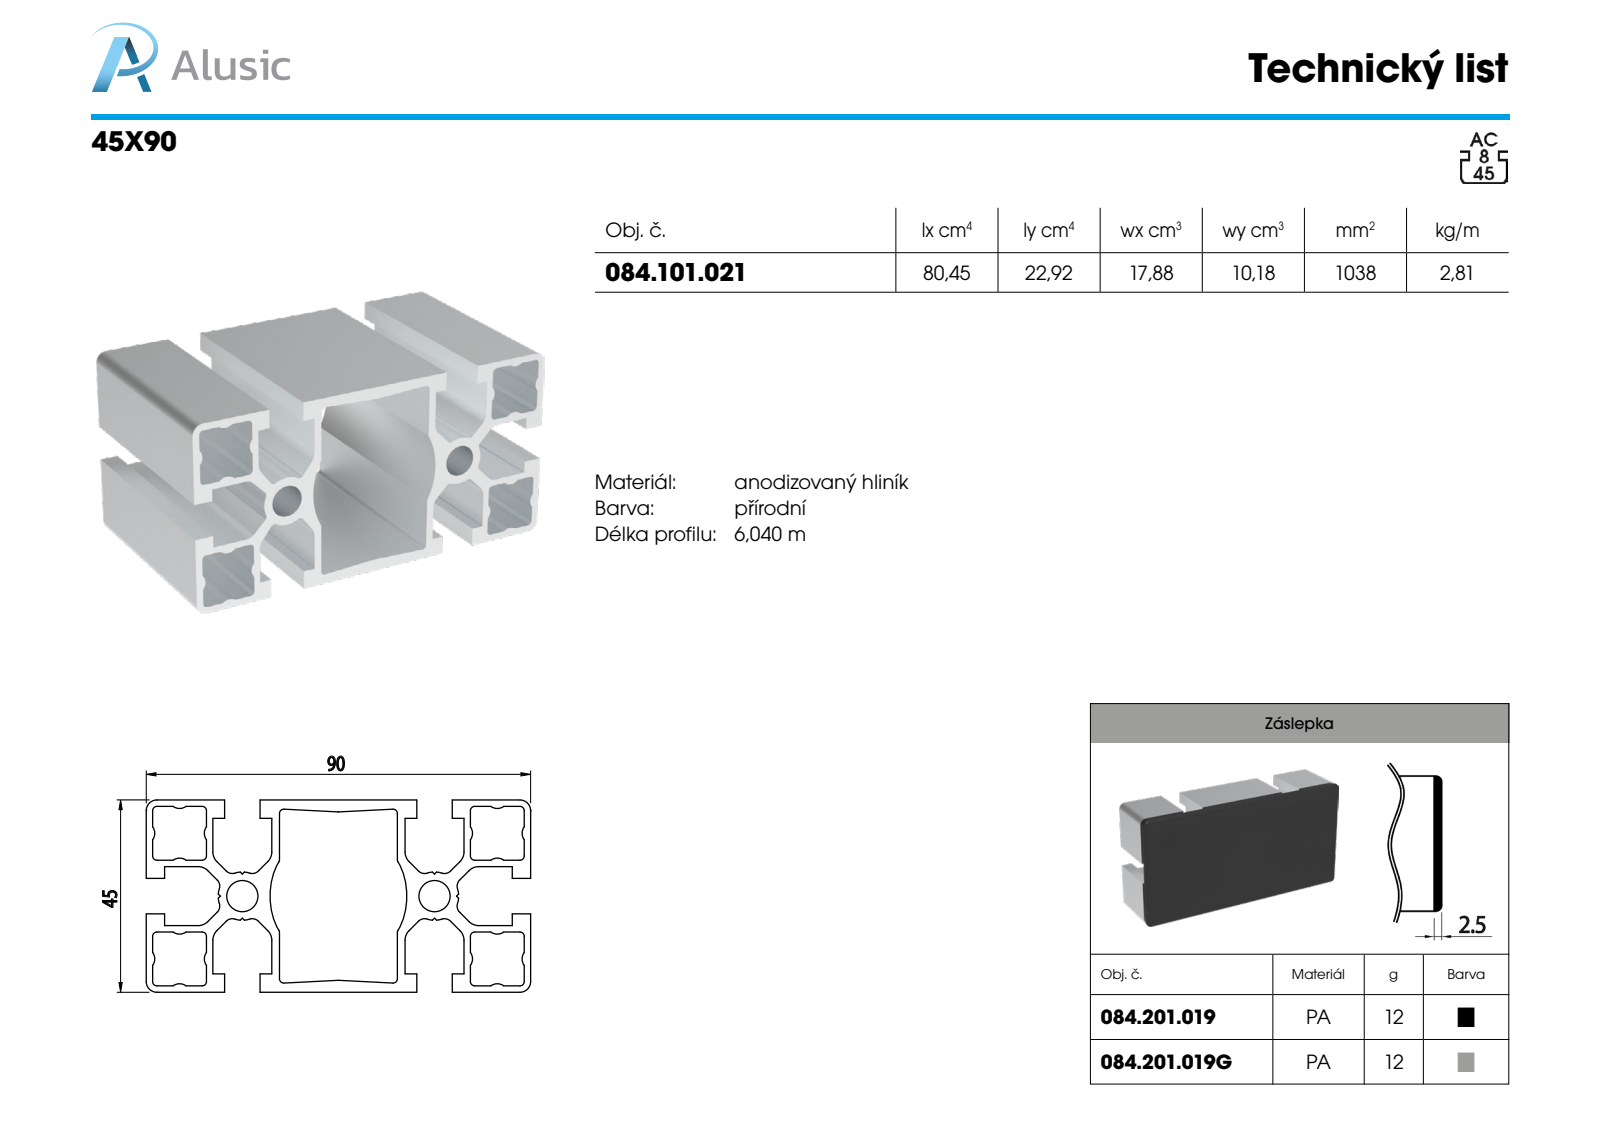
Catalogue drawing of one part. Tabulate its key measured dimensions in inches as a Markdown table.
| quantity | value |
| --- | --- |
| part name | 084.101.021 |
| STEP written by | SolidWorks 2018 (AUTOMOTIVE_DESIGN) |
| units | inches |
| bodies | 1 solid, 186 faces (100 planar, 86 cylindrical, 0 other) |
| overall size | 3.937 × 3.543 × 1.772 |
| volume | 6.075 in³ |
| surface area | 142 in² |
| round holes (diameter × count) | 0.287 × 2 |
| partial cylindrical surfaces (radius × count) | 0.039 × 32, 0.098 × 20, 0.118 × 12, 0.02 × 2, 0.222 × 2, 0.653 × 2 |
| main face-to-face distances | 1.772, 0.553, 0.108, 0.988, 0.614, 1.157, 0.061, 1.096, 0.557, 0.057 |
| hole center spacings | 1.772 |
